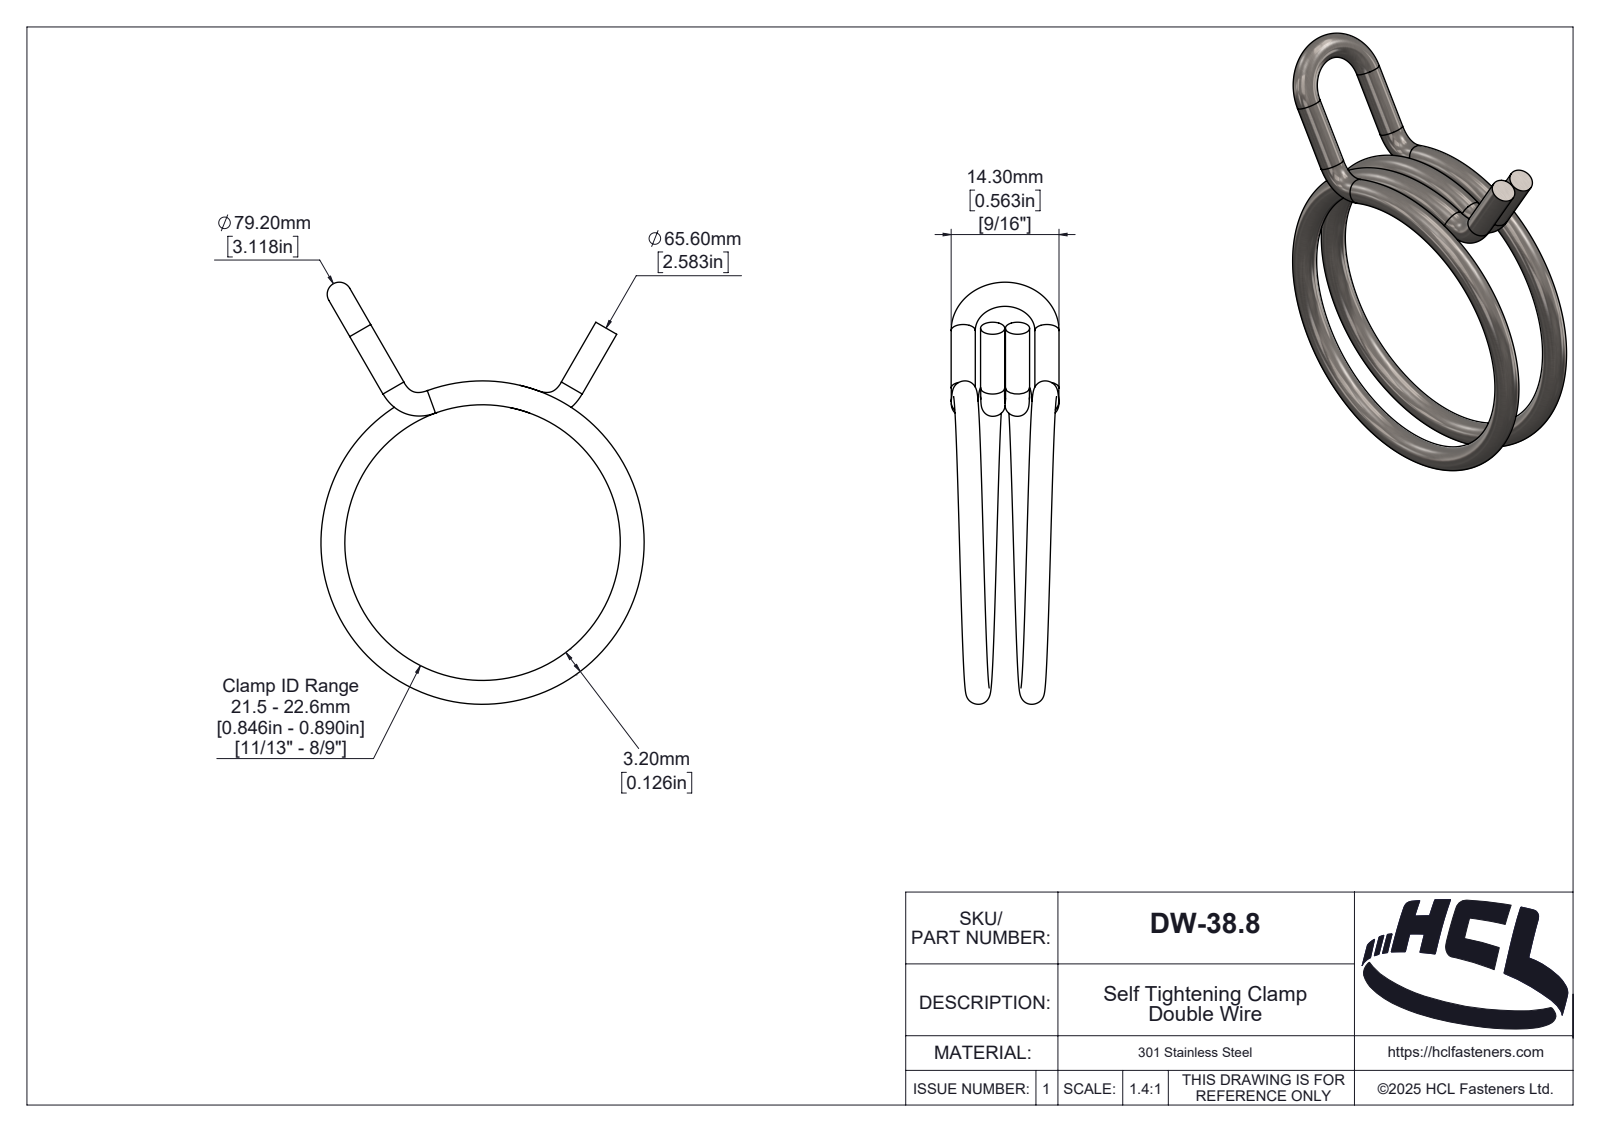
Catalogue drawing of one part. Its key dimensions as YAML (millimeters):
part_name: "DW-38.8"
step_written_by: "SolidWorks 2025 (AUTOMOTIVE_DESIGN)"
units: millimeters
bodies: {solids: 1, faces: 132, planar: 14, cylindrical: 53, other: 65}
overall_size: [55.94, 42.85, 14.3]
volume: 2809
surface_area: 3552
round_bosses_or_shafts:
  - {diameter: 3.2, count: 4}
partial_cylinders:
  - {radius: 0.16, count: 1}
  - {radius: 0.2, count: 1}
  - {radius: 0.21, count: 1}
  - {radius: 0.26, count: 1}
  - {radius: 0.36, count: 1}
  - {radius: 0.48, count: 1}
  - {radius: 0.6, count: 1}
  - {radius: 0.68, count: 1}
